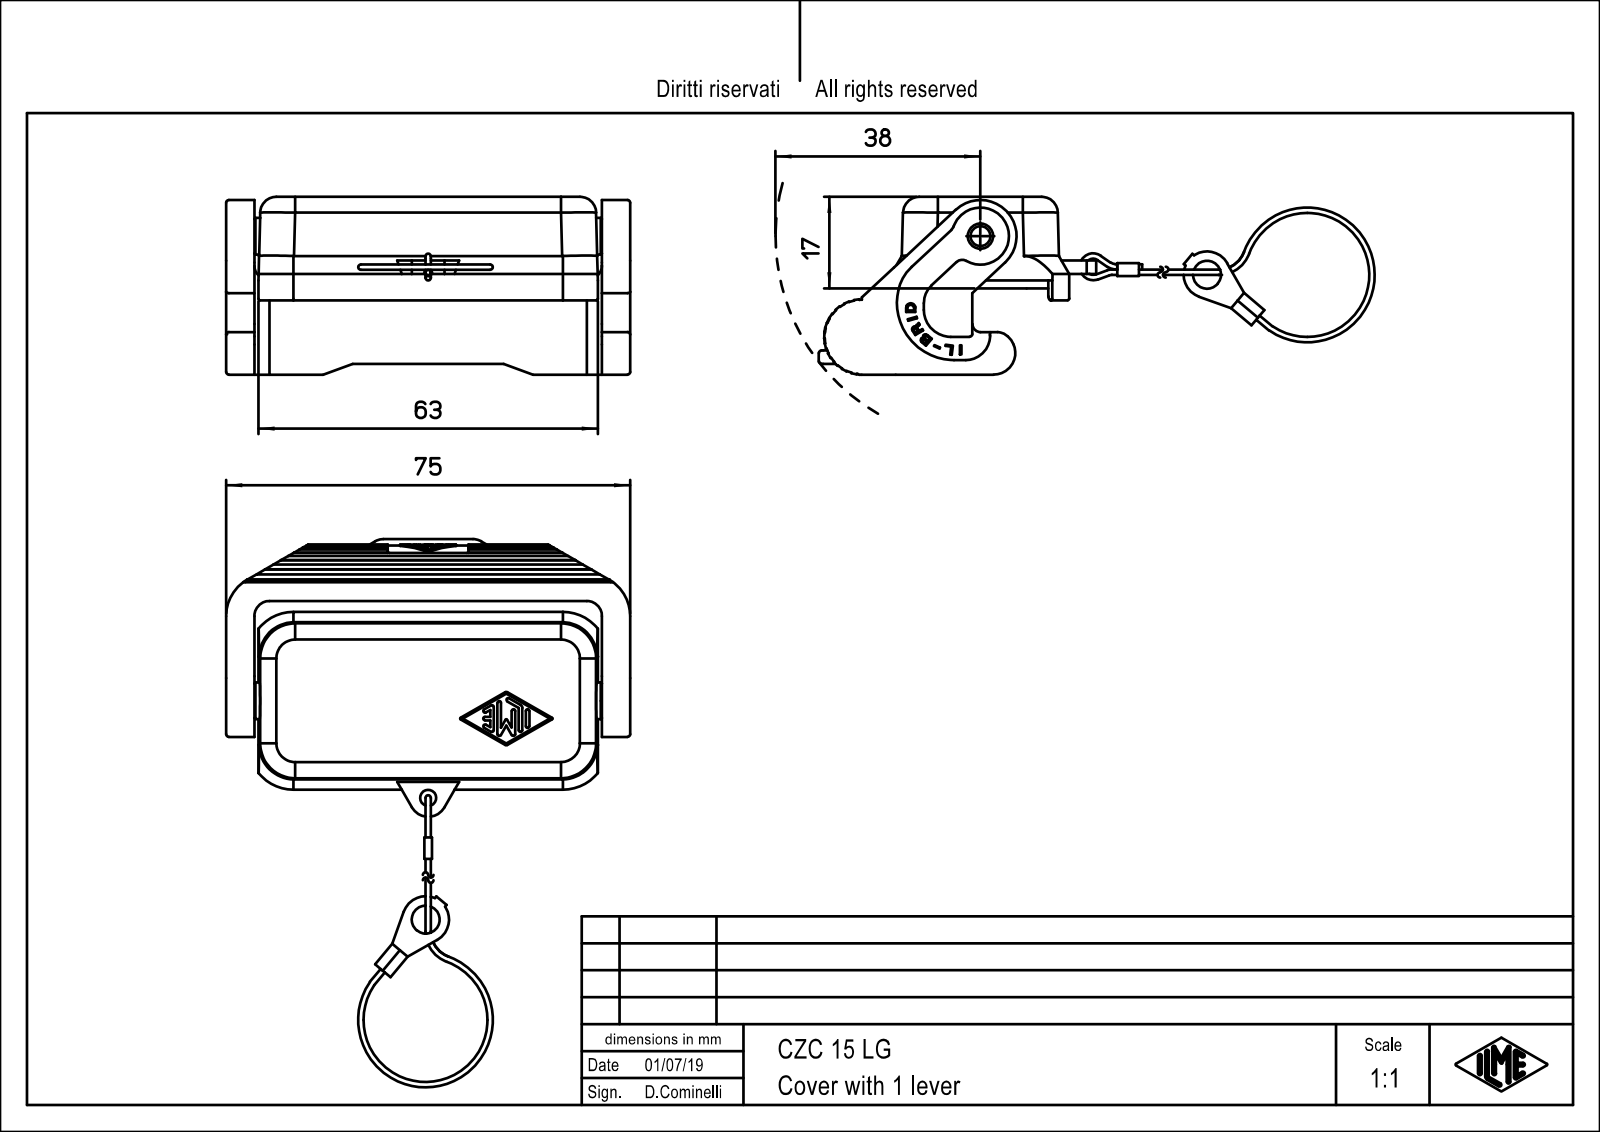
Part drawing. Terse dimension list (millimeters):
name: CZC_15_LG
written by: Creo Elements/Direct Modeling 20.1B 02-Apr-2019 (C) Parametric Technology GmbH (AUTOMOTIVE_DESIGN)
unit: mm
bodies: 1 solid, 445 faces (185 planar, 176 cylindrical, 84 other)
size: 75 × 51.5 × 33
volume: 23 955 mm³; area: 16 928 mm²
holes: 1× ⌀3
bosses: 1× ⌀6.8, 1× ⌀4.7
rounds: 31× R0.5, 15× R0.2, 12× R0.3, 7× R3, 5× R1, 4× R4.3, 4× R5.3, 4× R6.5
face distances: 2, 2.6, 15.5, 31, 33, 5.25, 64.5, 69.75, 2.55, 67.2
